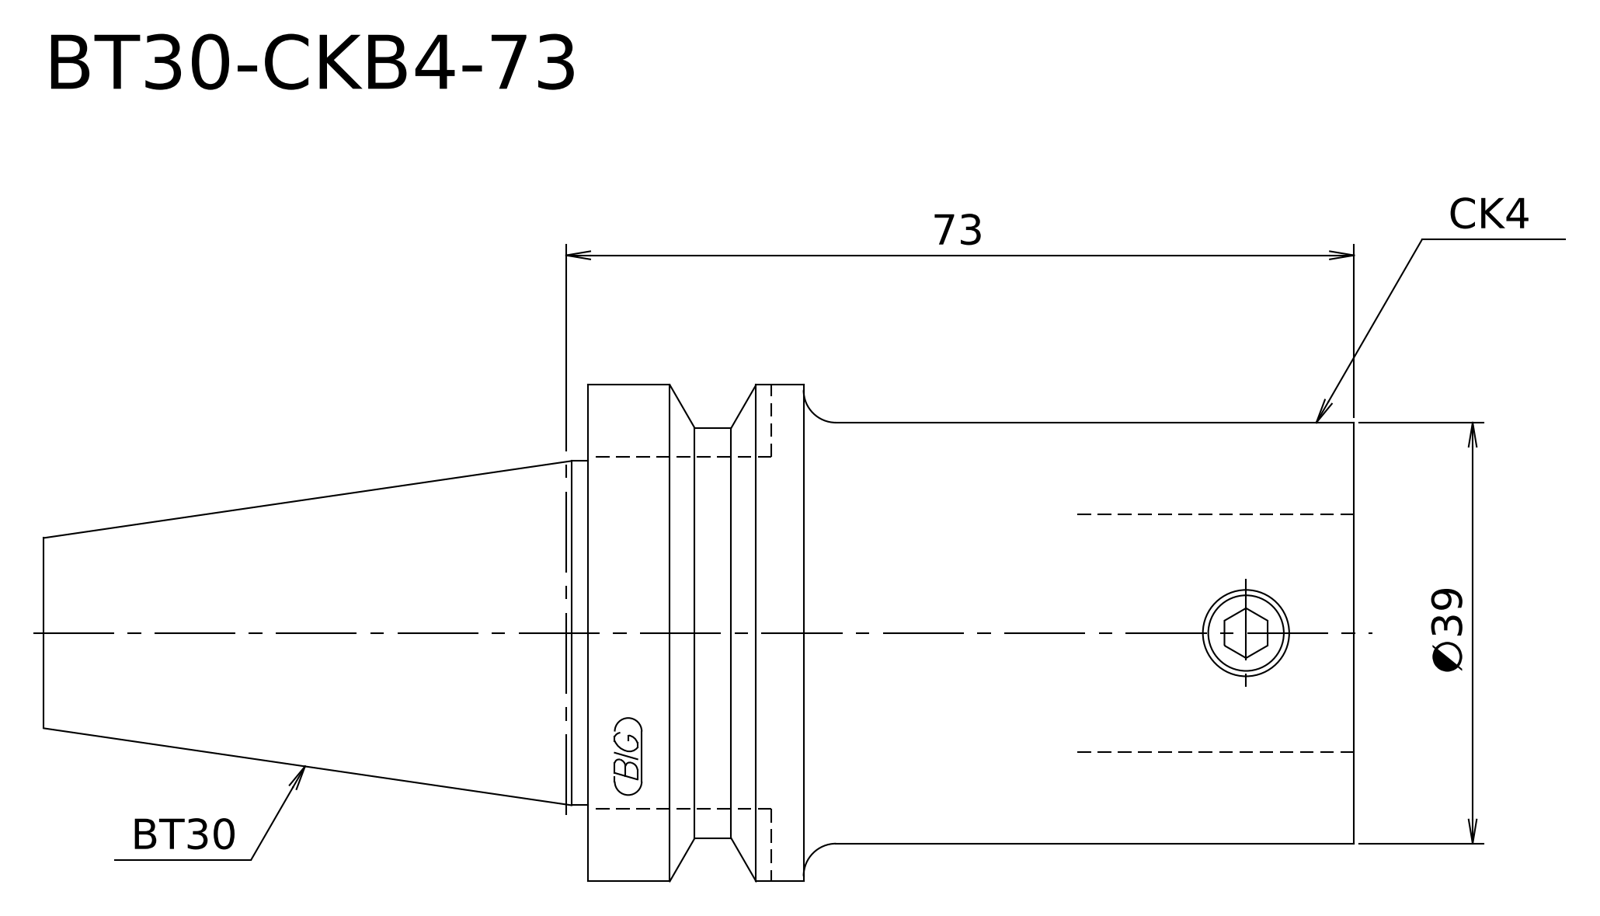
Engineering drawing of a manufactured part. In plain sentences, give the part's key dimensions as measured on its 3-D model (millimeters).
Its 3-D file was written by "Kubotek KeyCreator V8.5.1 (14335) (CONFIG_CONTROL_DESIGN)". It is 1 solid with 13 faces: 4 planar, 5 cylindrical and 4 other. Overall it measures 121.4 by 46 by 46 millimeters. Its volume is 117 040 cubic millimeters and its surface area 16 177 square millimeters. Round bosses or shafts: 1 of diameter 46, 1 of diameter 39, 1 of diameter 38, 1 of diameter 31.9. The main face-to-face distances are 71, 121.4, 50.4, 51, 20, 70.4.
